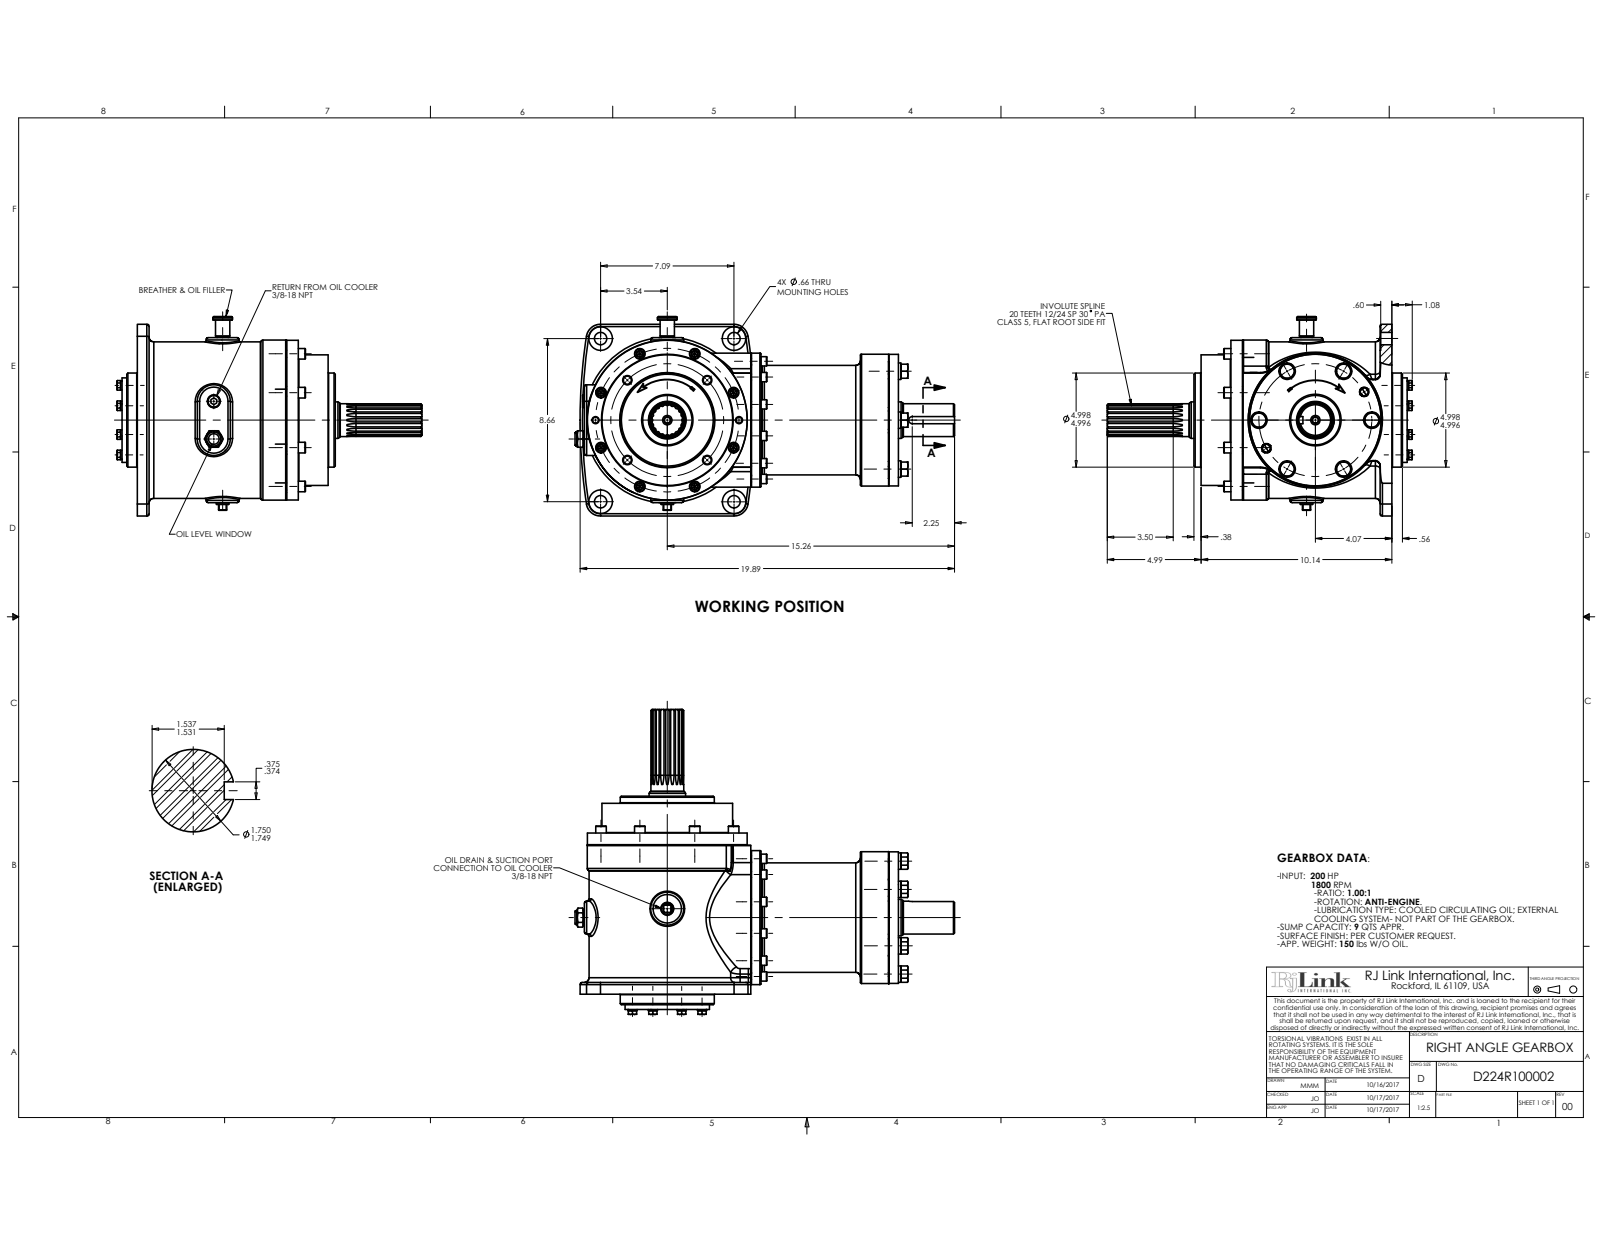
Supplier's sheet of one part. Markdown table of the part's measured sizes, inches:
| quantity | value |
| --- | --- |
| part name | D224014; PPSQM_38-18_6; HHCSZ_38-16X1_25_25; D224013 (+8 more) |
| STEP written by | SolidWorks 2017 (AUTOMOTIVE_DESIGN) |
| units | inches |
| bodies | 32 solids, 2512 faces (613 planar, 1235 cylindrical, 664 other) |
| overall size | 20.162 × 16.2 × 10.59 |
| volume | 153.4 in³ |
| surface area | 1 975 in² |
| round holes (diameter × count) | 0.257 × 14, 0.344 × 14, 0.422 × 12, 0.406 × 10, 0.203 × 8, 0.255 × 8, 0.281 × 8, 0.313 × 8, 0.438 × 8, 0.312 × 6, 0.509 × 6, 0.531 × 6 |
| round bosses / shafts (diameter × count) | 0.5 × 25, 0.312 × 14, 0.375 × 12, 0.375 × 12, 0.282 × 12, 0.562 × 8, 0.489 × 8, 0.437 × 8 |
| partial cylindrical surfaces (radius × count) | 0.019 × 50, 0.023 × 40, 0.25 × 17, 0.03 × 8, 0.12 × 6, 0.5 × 6, 0.38 × 4, 0.75 × 4 |
| main face-to-face distances | 0.625, 0.5, 7.285, 7.91, 0.52, 7.322, 7.842, 7.327, 7.329, 0.515 |
| hole center spacings | 3.234, 3, 2.784, 4.306, 5.415, 2.395, 0.846, 4.948 |
